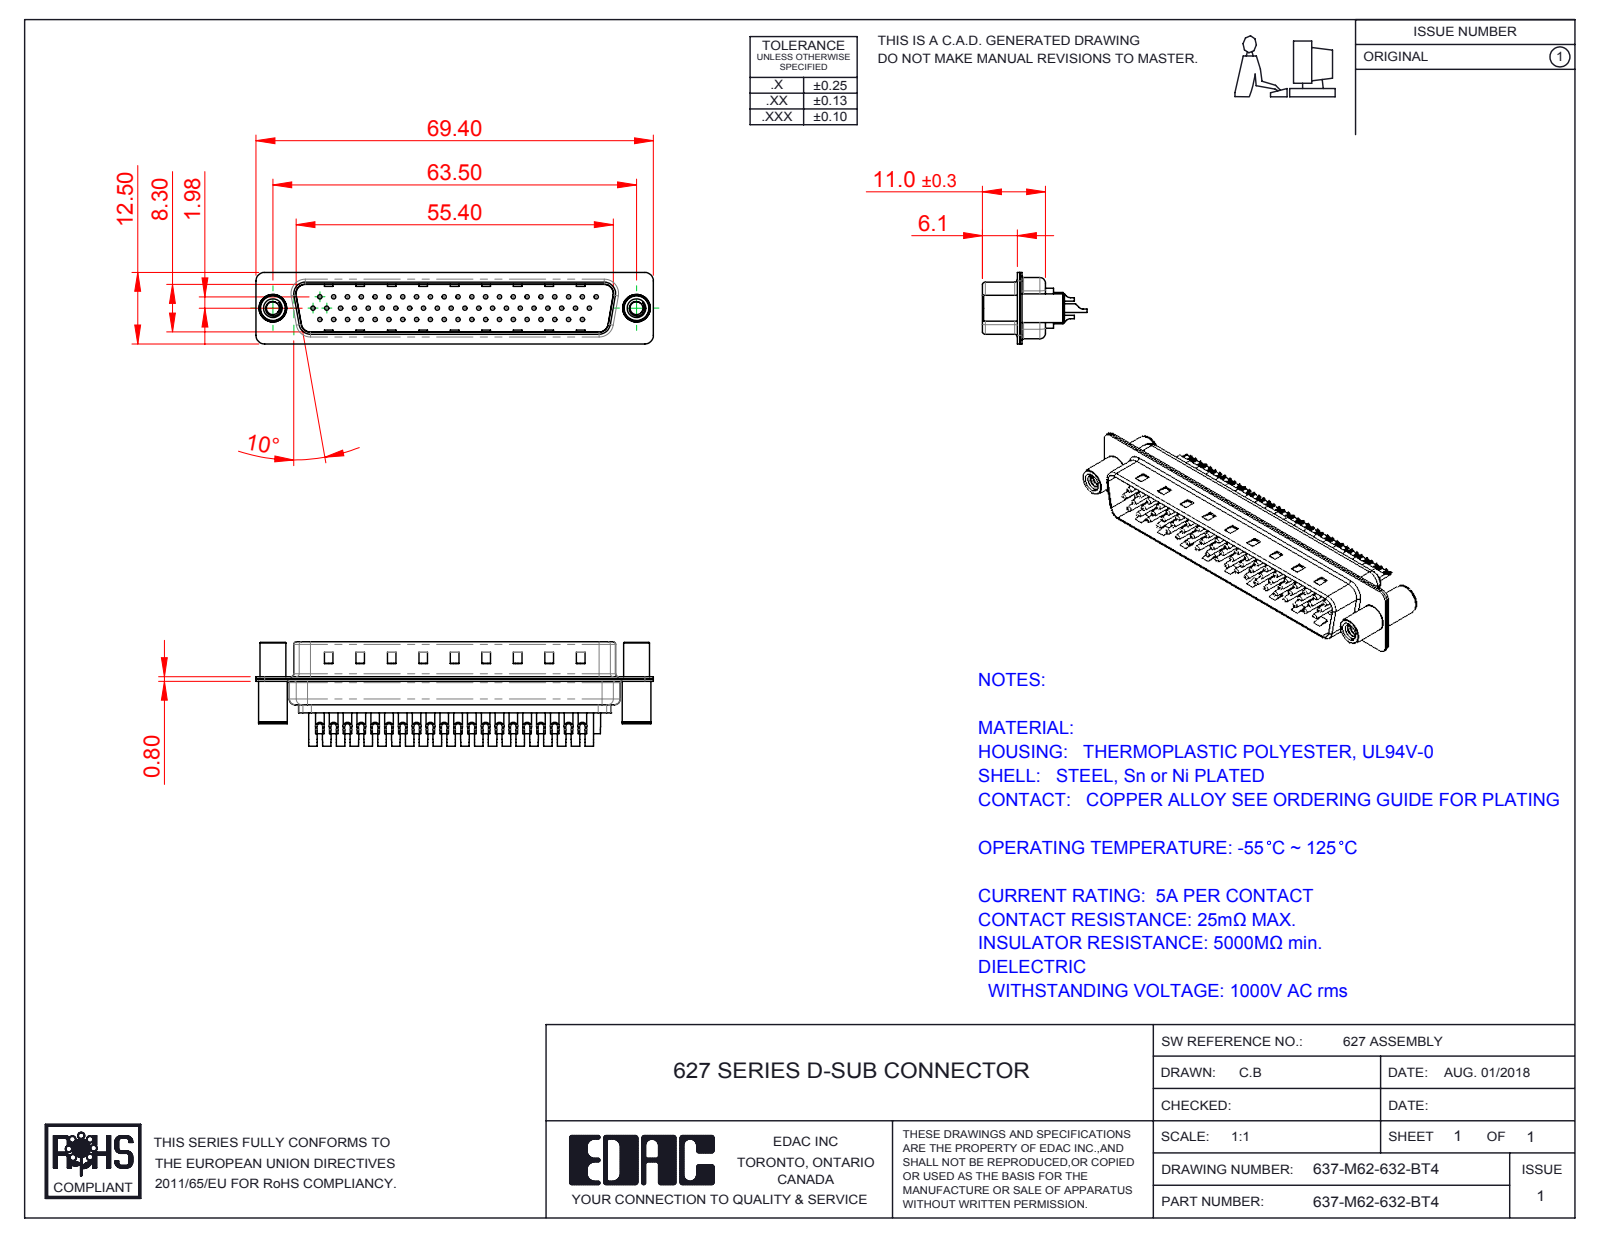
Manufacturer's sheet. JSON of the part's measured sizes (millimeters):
{"part_name": "637M Housing_62 Contacts; 637-M62-632-BT4; 637M Contact Row 2_32; 637M Contact Row 3_32 (+4 more)", "step_written_by": "SolidWorks 2016 (CONFIG_CONTROL_DESIGN)", "units": "millimeters", "bodies": {"solids": 67, "faces": 2792, "planar": 767, "cylindrical": 1185, "other": 840}, "overall_size": [69.4, 18.25, 12.5], "volume_mm3": 4409, "surface_area_mm2": 12706, "round_holes": [[0.75, 62], [1, 62], [1.6, 62], [2, 62], [2.26, 2], [3.26, 2], [4, 2], [4.8, 2]], "round_bosses_or_shafts": [[1.5, 62], [5, 2], [4.9, 2], [4.5, 2]], "partial_cylinders_radius": [[1.5, 16], [2, 12], [0.5, 8], [1.6, 8], [1, 7], [0.25, 4], [0.6, 4], [0.65, 4]], "face_to_face_distances": [0.4, 0.8, 9.5, 9.1, 8.7, 9.9, 0.75, 0.35, 1.2, 1.5], "hole_center_spacings": [7.24, 2.32, 2.41, 4.13, 9.65, 4.83, 14.48, 11.04]}
